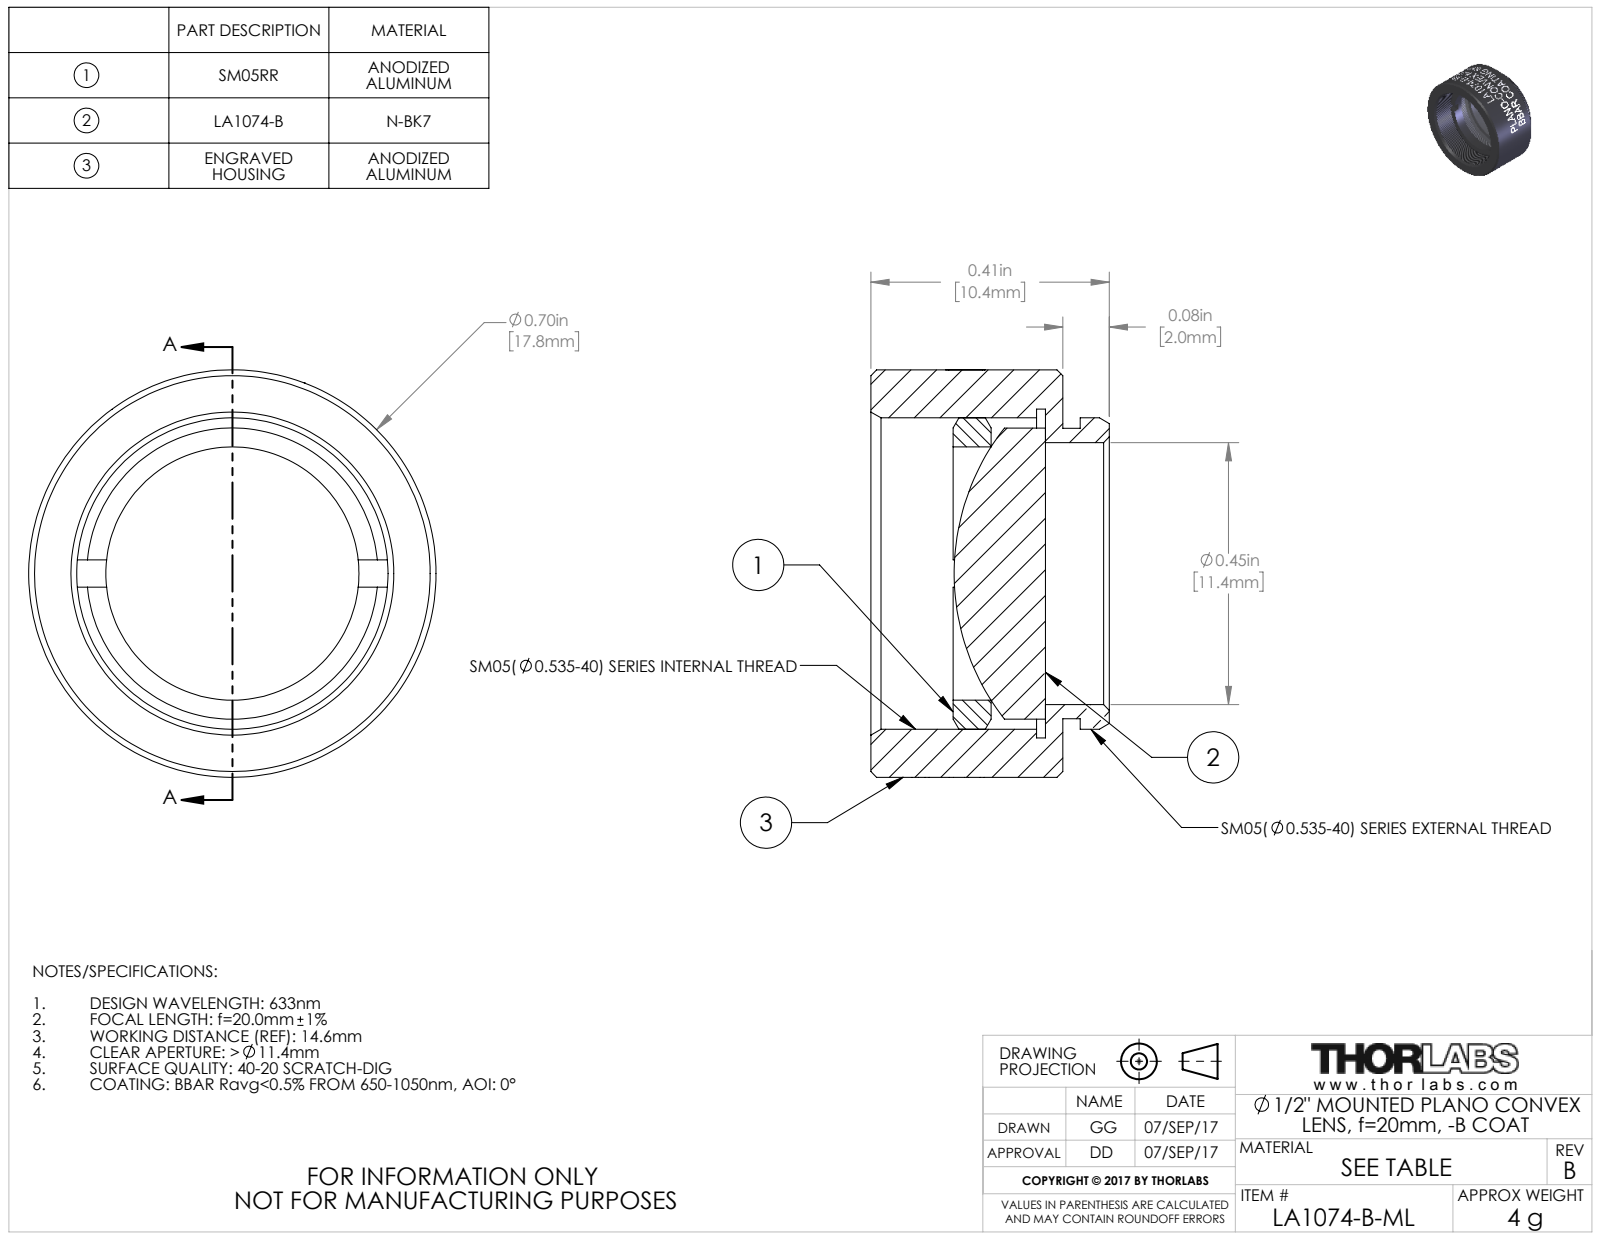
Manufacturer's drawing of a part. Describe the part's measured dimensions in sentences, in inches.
The part is named "24392-E0W". Its 3-D file was written by "SolidWorks 2016 (CONFIG_CONTROL_DESIGN)". It is 3 solids with 279 faces: 94 planar, 110 cylindrical and 75 other. Overall it measures 0.7 by 0.7 by 0.41 inches. Its volume is 0.085 cubic inches and its surface area 2.874 square inches. Round holes: 1 of diameter 0.435, 1 of diameter 0.45, 1 of diameter 0.535, 1 of diameter 0.565. Round bosses or shafts: 1 of diameter 0.7, 1 of diameter 0.535, 1 of diameter 0.5, 1 of diameter 0.499. Partial cylindrical surfaces (rounded edges, fillets, slot ends): 1 of radius 0.35. The main face-to-face distances are 0.03, 0.3, 0.33, 0.124, 0.093, 0.207, 0.158, 0.189, 0.065, 0.142.
